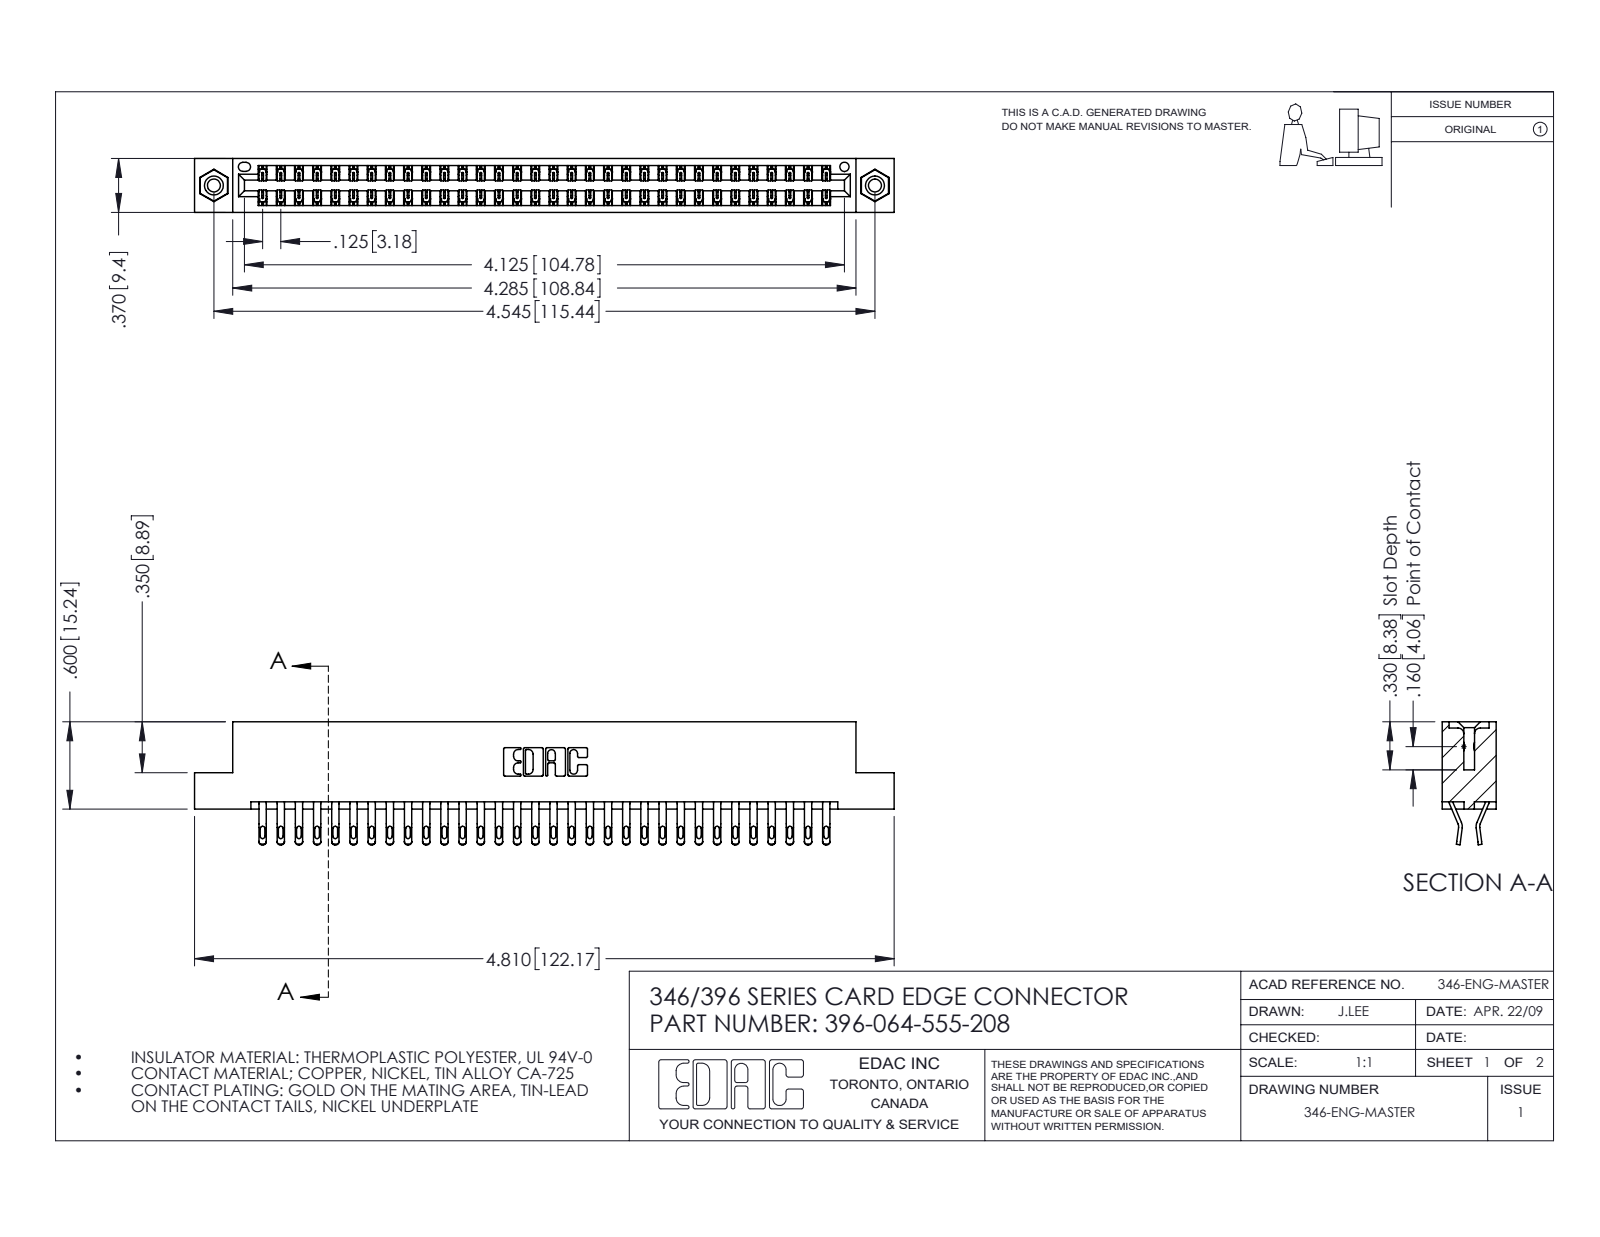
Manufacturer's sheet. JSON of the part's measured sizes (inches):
{"part_name": "345-292-001_555 Tail; 346 Part_Flush Mounting Lugs - 0.156 Dia-TI; 345-250-001_345-250-003-102; 396-064-555-208", "step_written_by": "SolidWorks 2016 (CONFIG_CONTROL_DESIGN)", "units": "inches", "bodies": {"solids": 67, "faces": 3894, "planar": 2220, "cylindrical": 1658, "other": 16}, "overall_size": [4.81, 0.845, 0.37], "volume_in3": 0.733, "surface_area_in2": 26.41, "round_holes": [[0.089, 2], [0.125, 2], [0.156, 2], [0.064, 1]], "round_bosses_or_shafts": [[0.155, 2]], "partial_cylinders_radius": [[0.016, 128], [0.02, 128], [0.006, 96], [0.01, 22], [0.007, 6], [0.031, 6], [0.026, 3], [0.01, 2]], "face_to_face_distances": [0.048, 0.322, 0.37, 0.25, 0.025, 0.072, 0.298, 0.275, 0.148, 0.222], "hole_center_spacings": [0.246, 4.337, 4.545]}
